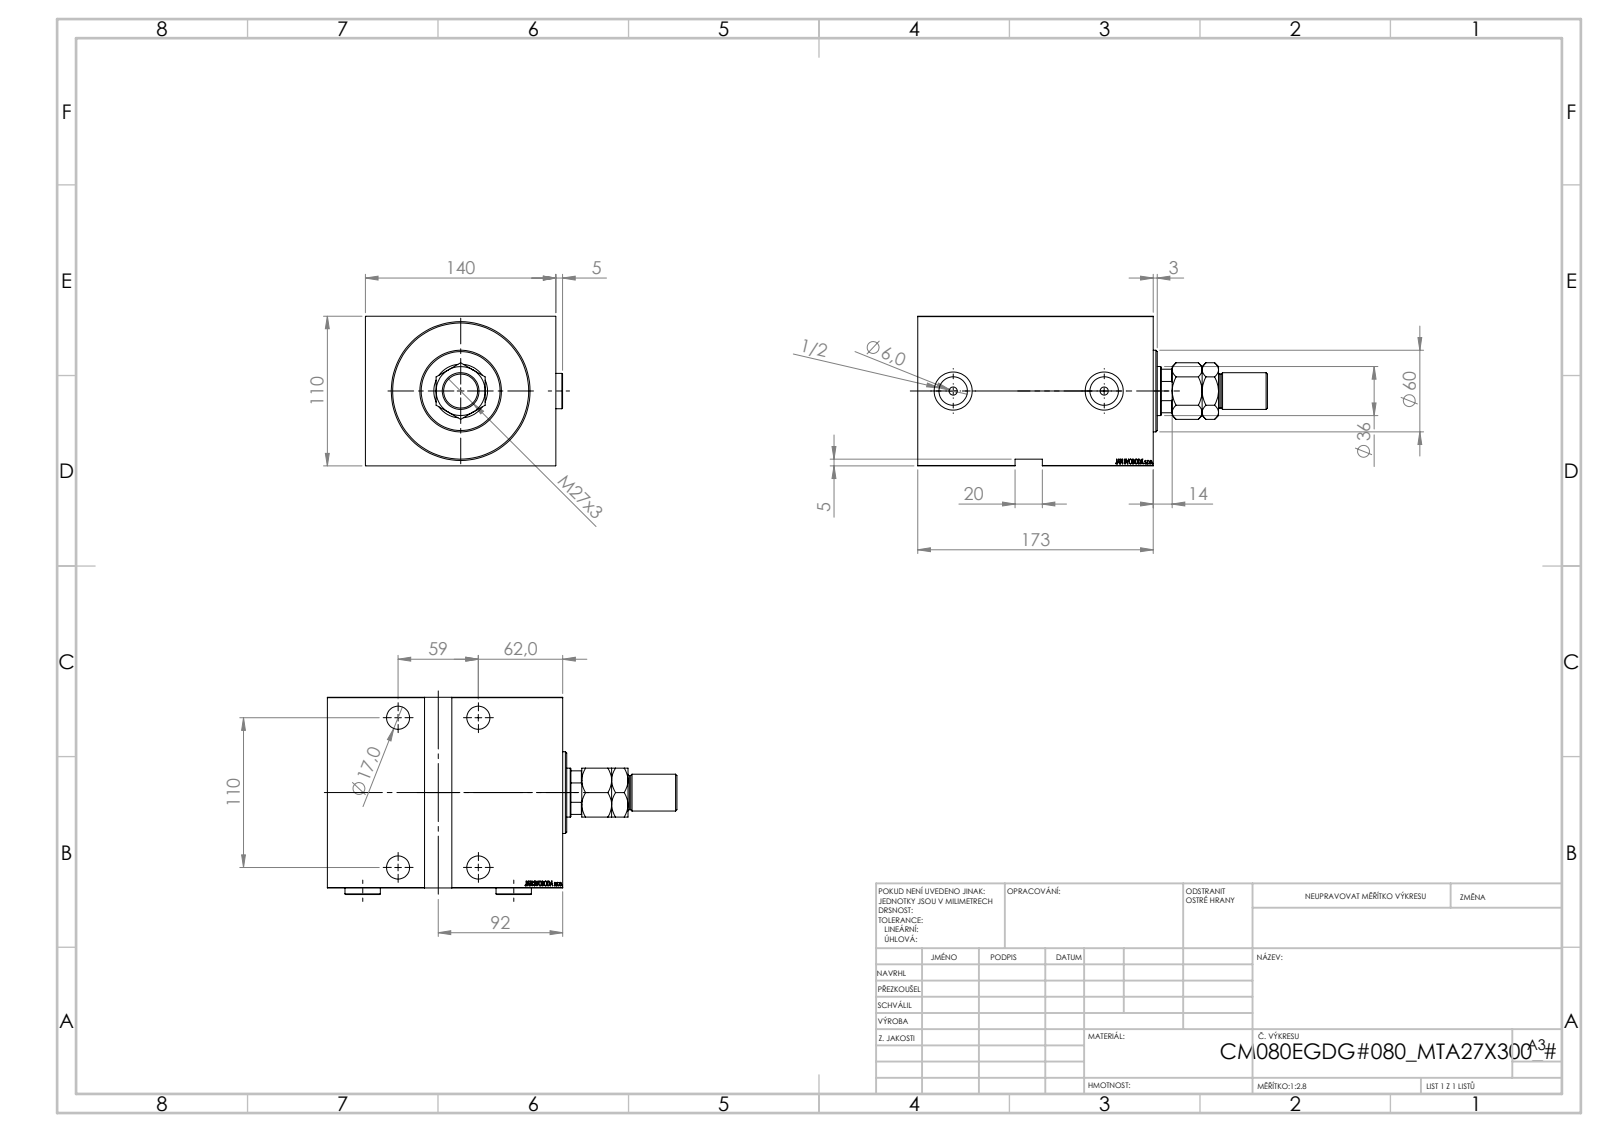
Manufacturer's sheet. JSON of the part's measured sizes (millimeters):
{"part_name": "V450CM_VC_B; Zatka_OIL_PORT; MTA; V450CM_E_VCP (+1 more)", "step_written_by": "SolidWorks 2019 (CONFIG_CONTROL_DESIGN)", "units": "millimeters", "bodies": {"solids": 6, "faces": 961, "planar": 461, "cylindrical": 72, "other": 428}, "overall_size": [257, 144.9, 110], "volume_mm3": 2260000, "surface_area_mm2": 258275, "round_holes": [[17, 4], [25, 4], [6, 2], [20.96, 2], [28, 2], [25.5, 1], [36, 1], [39.5, 1], [80, 1], [100, 1]], "round_bosses_or_shafts": [[26, 2], [82, 1], [60, 1], [27, 1], [25, 1]], "partial_cylinders_radius": [[17.5, 1]], "face_to_face_distances": [110, 140, 173, 21, 152, 5, 168, 147, 79, 89], "hole_center_spacings": [59, 110, 124.82, 111]}
